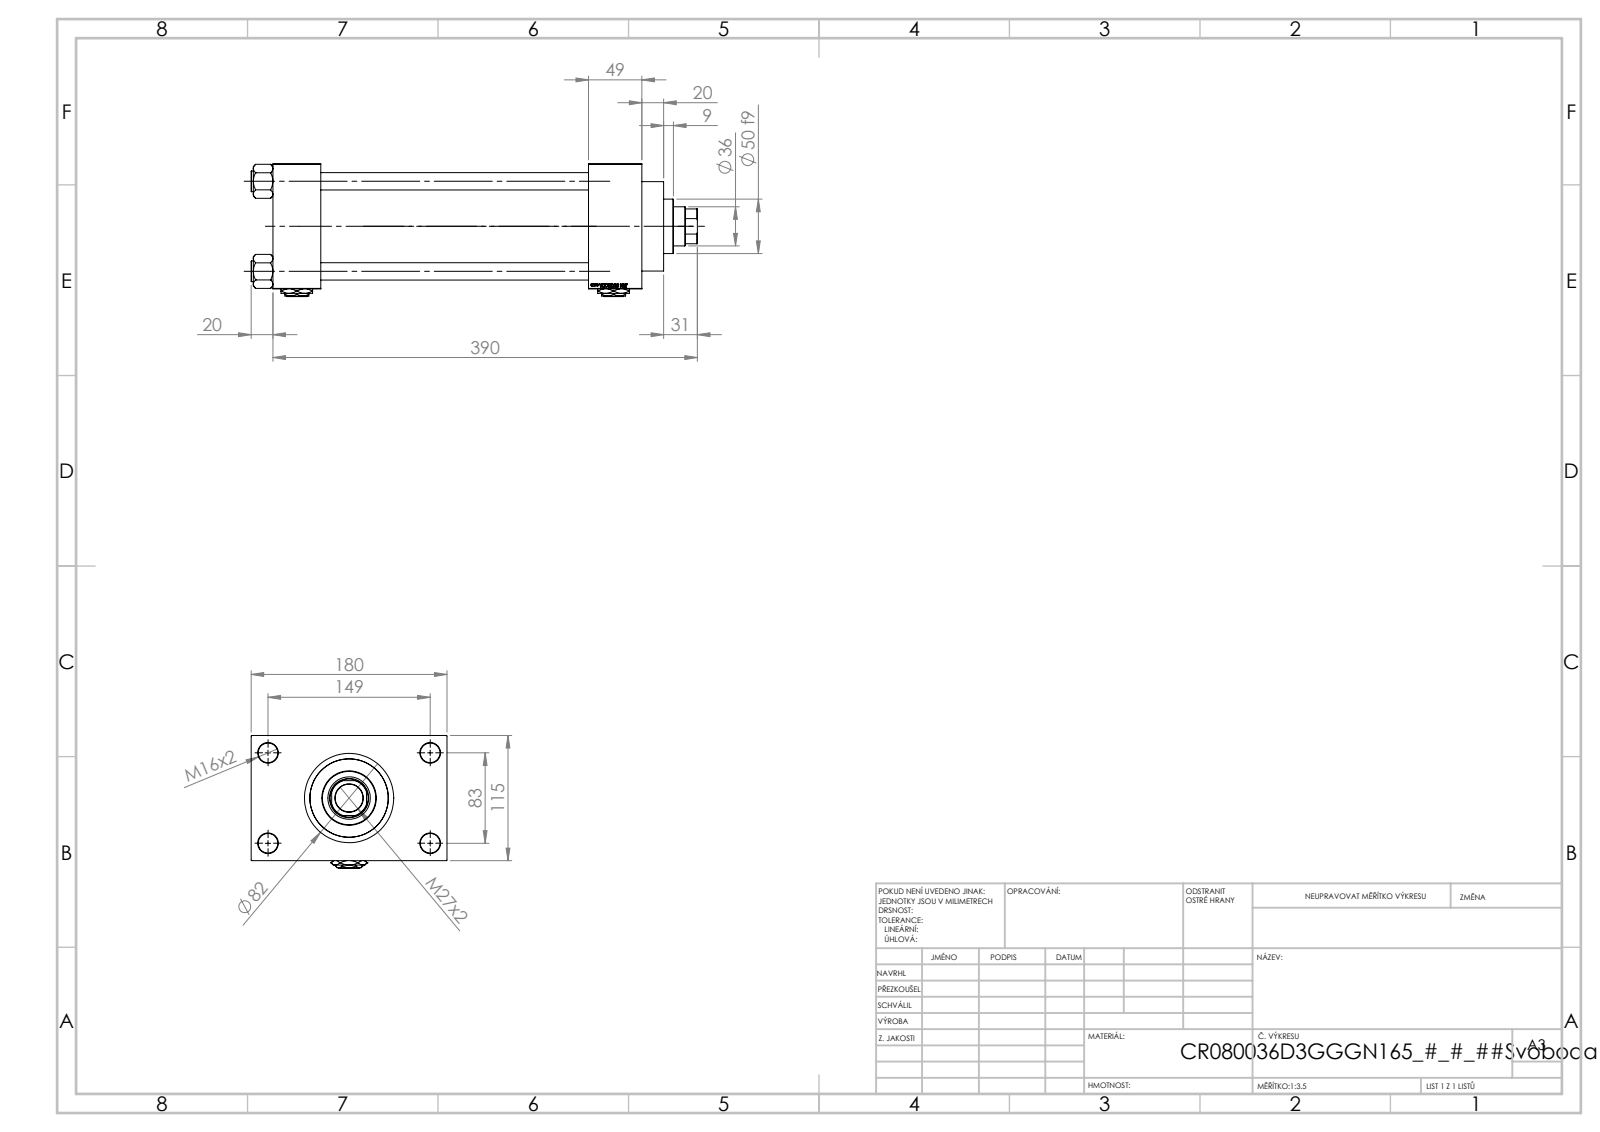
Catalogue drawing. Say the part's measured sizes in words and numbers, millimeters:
The part is named "V215_VC_A; NUT_M5_D; V215CR_D_TYCINKA; V215CR_D_Body (+2 more)". Its 3-D file was written by "SolidWorks 2019 (CONFIG_CONTROL_DESIGN)". It is 13 solids with 1253 faces: 593 planar, 100 cylindrical and 560 other. Overall it measures 410 by 180 by 122 millimeters. Its volume is 2 452 000 cubic millimeters and its surface area 451 033 square millimeters. Round holes: 4 of diameter 16, 4 of diameter 18, 2 of diameter 7, 2 of diameter 26.44, 2 of diameter 35, 1 of diameter 25.5, 1 of diameter 36, 1 of diameter 39, 1 of diameter 61, 1 of diameter 72, 1 of diameter 80. Round bosses or shafts: 4 of diameter 19, 1 of diameter 86, 1 of diameter 82, 1 of diameter 50. Partial cylindrical surfaces (rounded edges, fillets, slot ends): 1 of radius 17.5. The main face-to-face distances are 115, 246, 295, 49, 44, 290, 339, 32.5, 147.5, 180. The hole center spacings are 33.15, 58.48, 82.7, 85.28, 89.24, 115.85, 142.43, 83.
